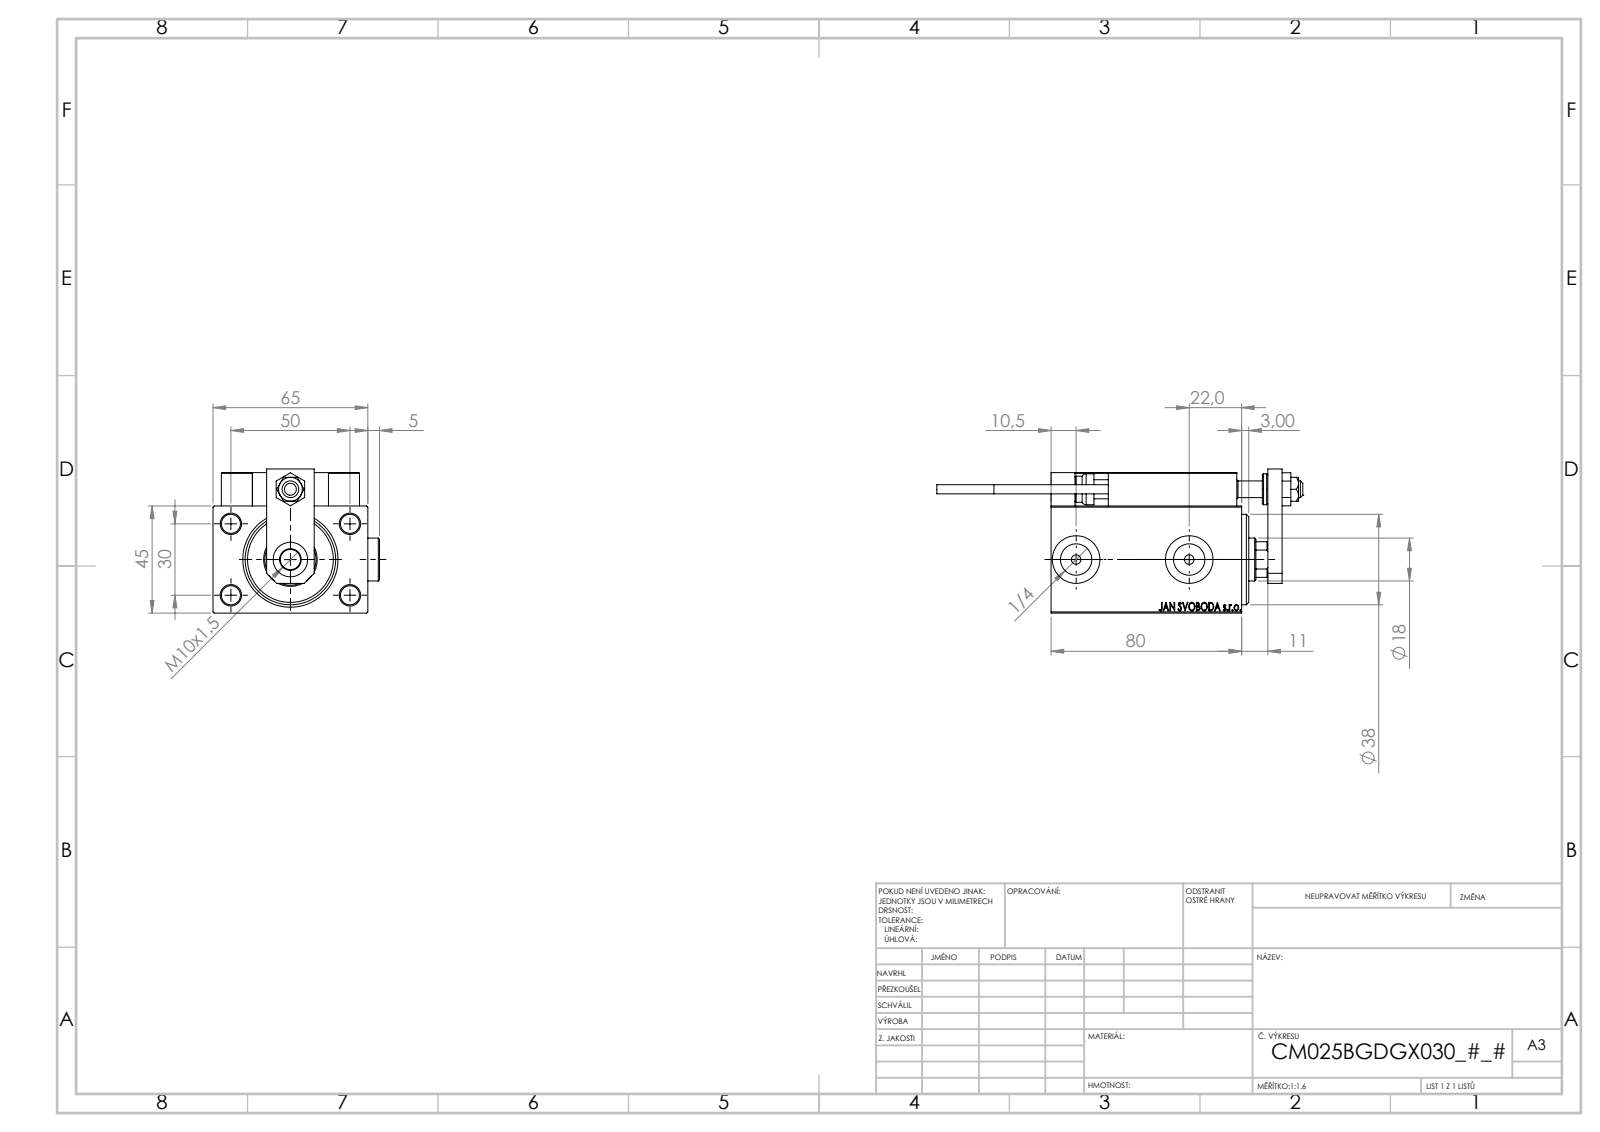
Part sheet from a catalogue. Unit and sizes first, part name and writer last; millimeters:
Units: millimetres
Overall size (bounding box): 153.7 × 69.9 × 60.5
Round holes (diameter × count): ⌀8 ×9, ⌀4 ×6, ⌀3.2 ×4, ⌀5 ×2, ⌀13.16 ×2, ⌀20 ×2, ⌀7 ×1, ⌀8.5 ×1, ⌀14.5 ×1, ⌀18 ×1, ⌀21.5 ×1, ⌀22.5 ×1
Round bosses / shafts (diameter × count): ⌀18 ×2, ⌀5 ×2, ⌀3.8 ×2, ⌀13 ×1, ⌀11 ×1
Partial cylindrical surfaces — rounded edges, fillets, slot ends (radius × count): R0.3 ×30, R3 ×2, R8.5 ×1
Main face-to-face distances: 45, 14, 65, 6, 59, 5, 13, 3.5, 91, 19
Hole centre spacings: 29.15, 11.37, 20, 28.9, 29.59, 29.69, 30, 32.06
Volume: 264 882 mm³ · Surface area: 71 011 mm²
Bodies: 26 solids, 1372 faces (595 planar, 200 cylindrical, 577 other)
Part name (STEP PRODUCT): NUT_D10; SWITCH DIM B,W; NUT_D12; ALLEN BOLT D5 (+7 more)
STEP written by: SolidWorks 2019 (CONFIG_CONTROL_DESIGN)
